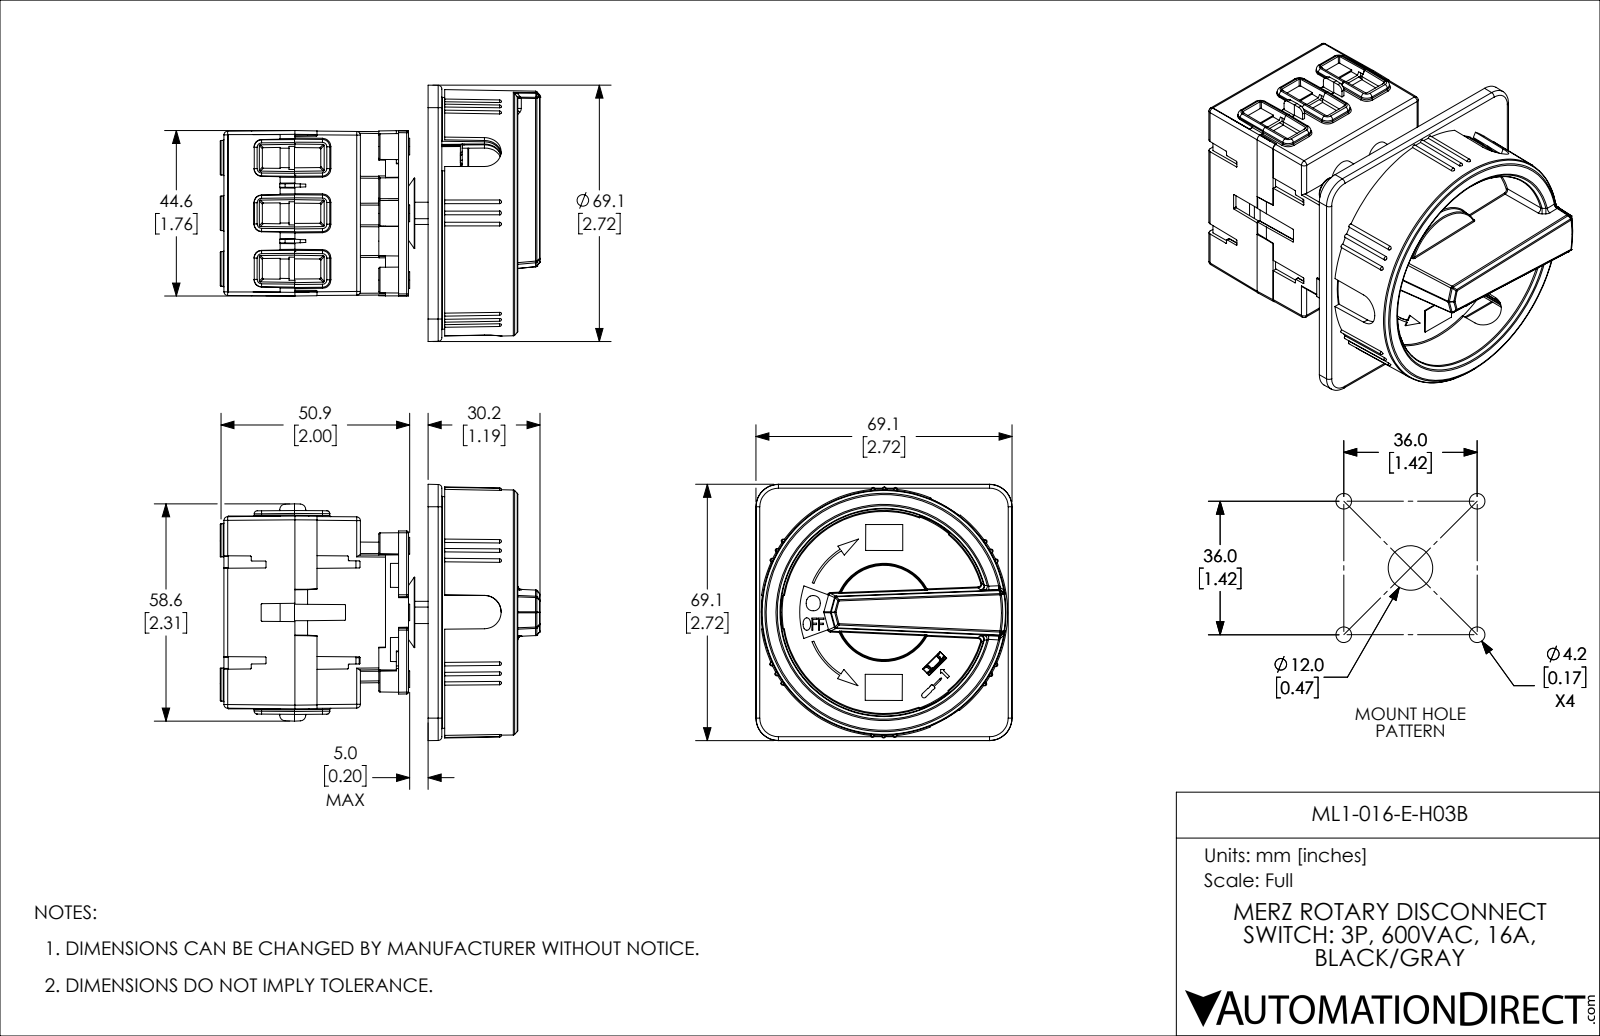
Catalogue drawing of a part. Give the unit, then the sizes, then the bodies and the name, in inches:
Units: inches
Overall size (bounding box): 3.398 × 2.722 × 2.722
Round bosses / shafts (diameter × count): ⌀0.071 ×2, ⌀0.748 ×1, ⌀0.236 ×1
Partial cylindrical surfaces — rounded edges, fillets, slot ends (radius × count): R0.02 ×132, R0.012 ×68, R0.039 ×50, R0.008 ×44, R0.008 ×41, R0.01 ×39, R0.031 ×34, R0.079 ×12
Main face-to-face distances: 0.059, 0.138, 0.197, 0.079, 0.276, 0.571, 0.02, 0.551, 0.295, 0.807
Volume: 8.361 in³ · Surface area: 101.4 in²
Bodies: 1 solid, 2964 faces (1185 planar, 610 cylindrical, 1169 other)
Part name (STEP PRODUCT): ML1-016-E-H03B
STEP written by: SolidWorks 2019 (AUTOMOTIVE_DESIGN)
